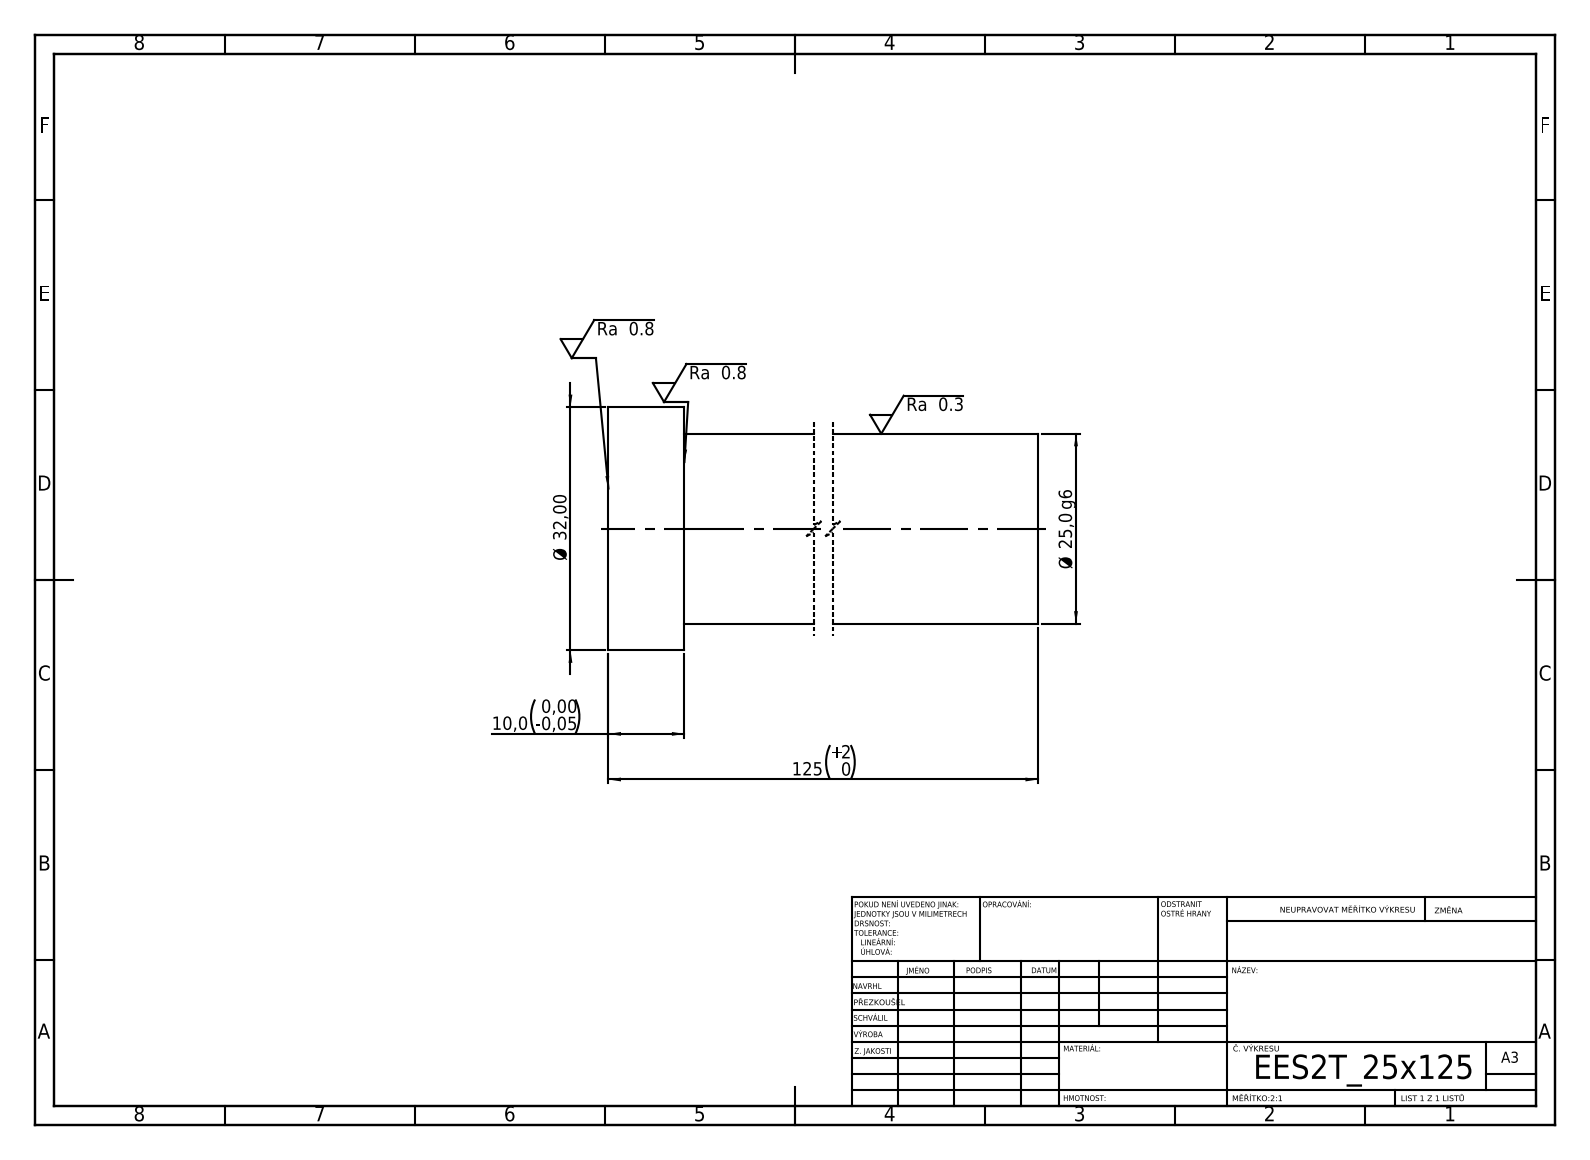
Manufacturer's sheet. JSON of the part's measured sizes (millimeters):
{"step_written_by": "SolidWorks 2019 (CONFIG_CONTROL_DESIGN)", "units": "millimeters", "bodies": {"solids": 1, "faces": 7, "planar": 3, "cylindrical": 4, "other": 0}, "overall_size": [125, 32, 32], "volume_mm3": 64493, "surface_area_mm2": 11646, "round_bosses_or_shafts": [[32, 1], [25, 1]], "face_to_face_distances": [125, 10, 115]}
